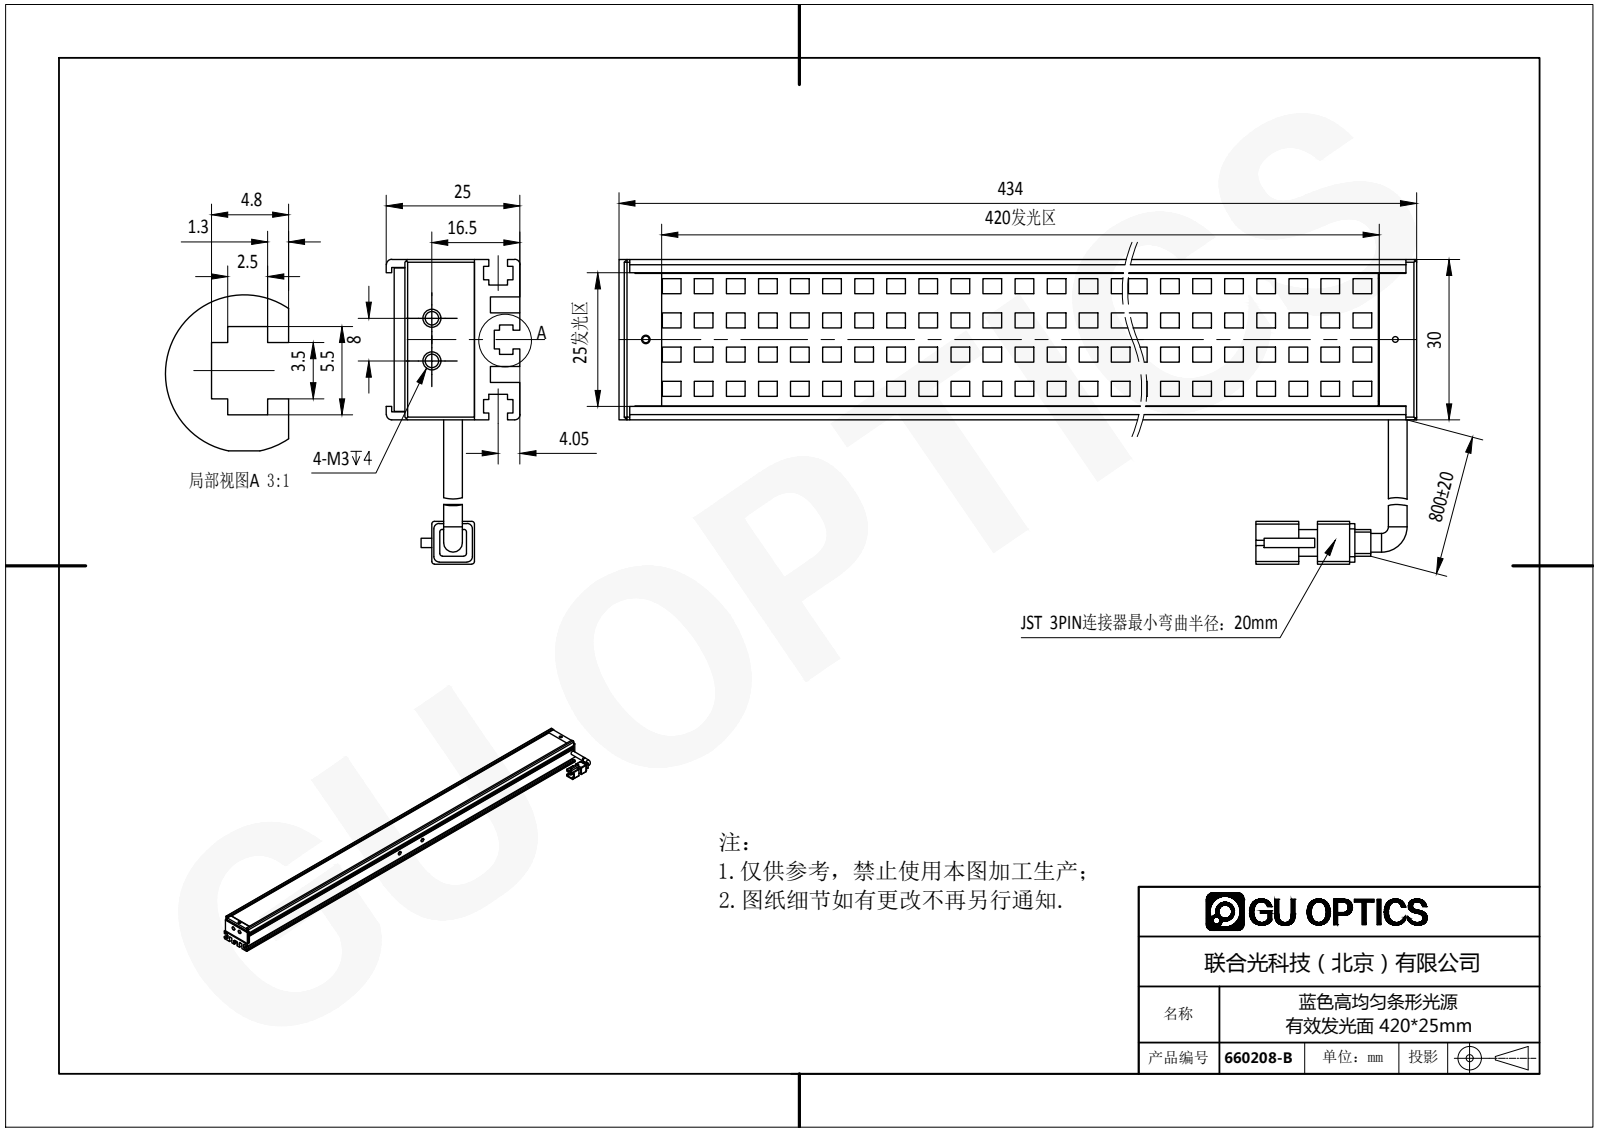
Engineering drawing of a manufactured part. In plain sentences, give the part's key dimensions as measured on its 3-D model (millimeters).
The part is named "660208-B". Its 3-D file was written by "SolidWorks 2016 (AUTOMOTIVE_DESIGN)". It is 6 solids with 1842 faces: 1656 planar, 83 cylindrical and 103 other. Overall it measures 434 by 57 by 25 millimeters. Its volume is 145 249 cubic millimeters and its surface area 148 514 square millimeters. Round holes: 5 of diameter 1.6, 2 of diameter 1.5, 2 of diameter 1.7, 2 of diameter 2.5, 2 of diameter 2.8, 2 of diameter 3, 1 of diameter 1.1, 1 of diameter 1.25, 1 of diameter 2. Round bosses or shafts: 2 of diameter 3.5. Partial cylindrical surfaces (rounded edges, fillets, slot ends): 12 of radius 1, 8 of radius 0.5, 1 of radius 1.65. The main face-to-face distances are 1, 2, 13, 2.5, 3, 27.5, 9.5, 4.5, 12, 15.1. The hole center spacings are 425, 7, 425.06, 8, 30, 197, 197.11, 198.
